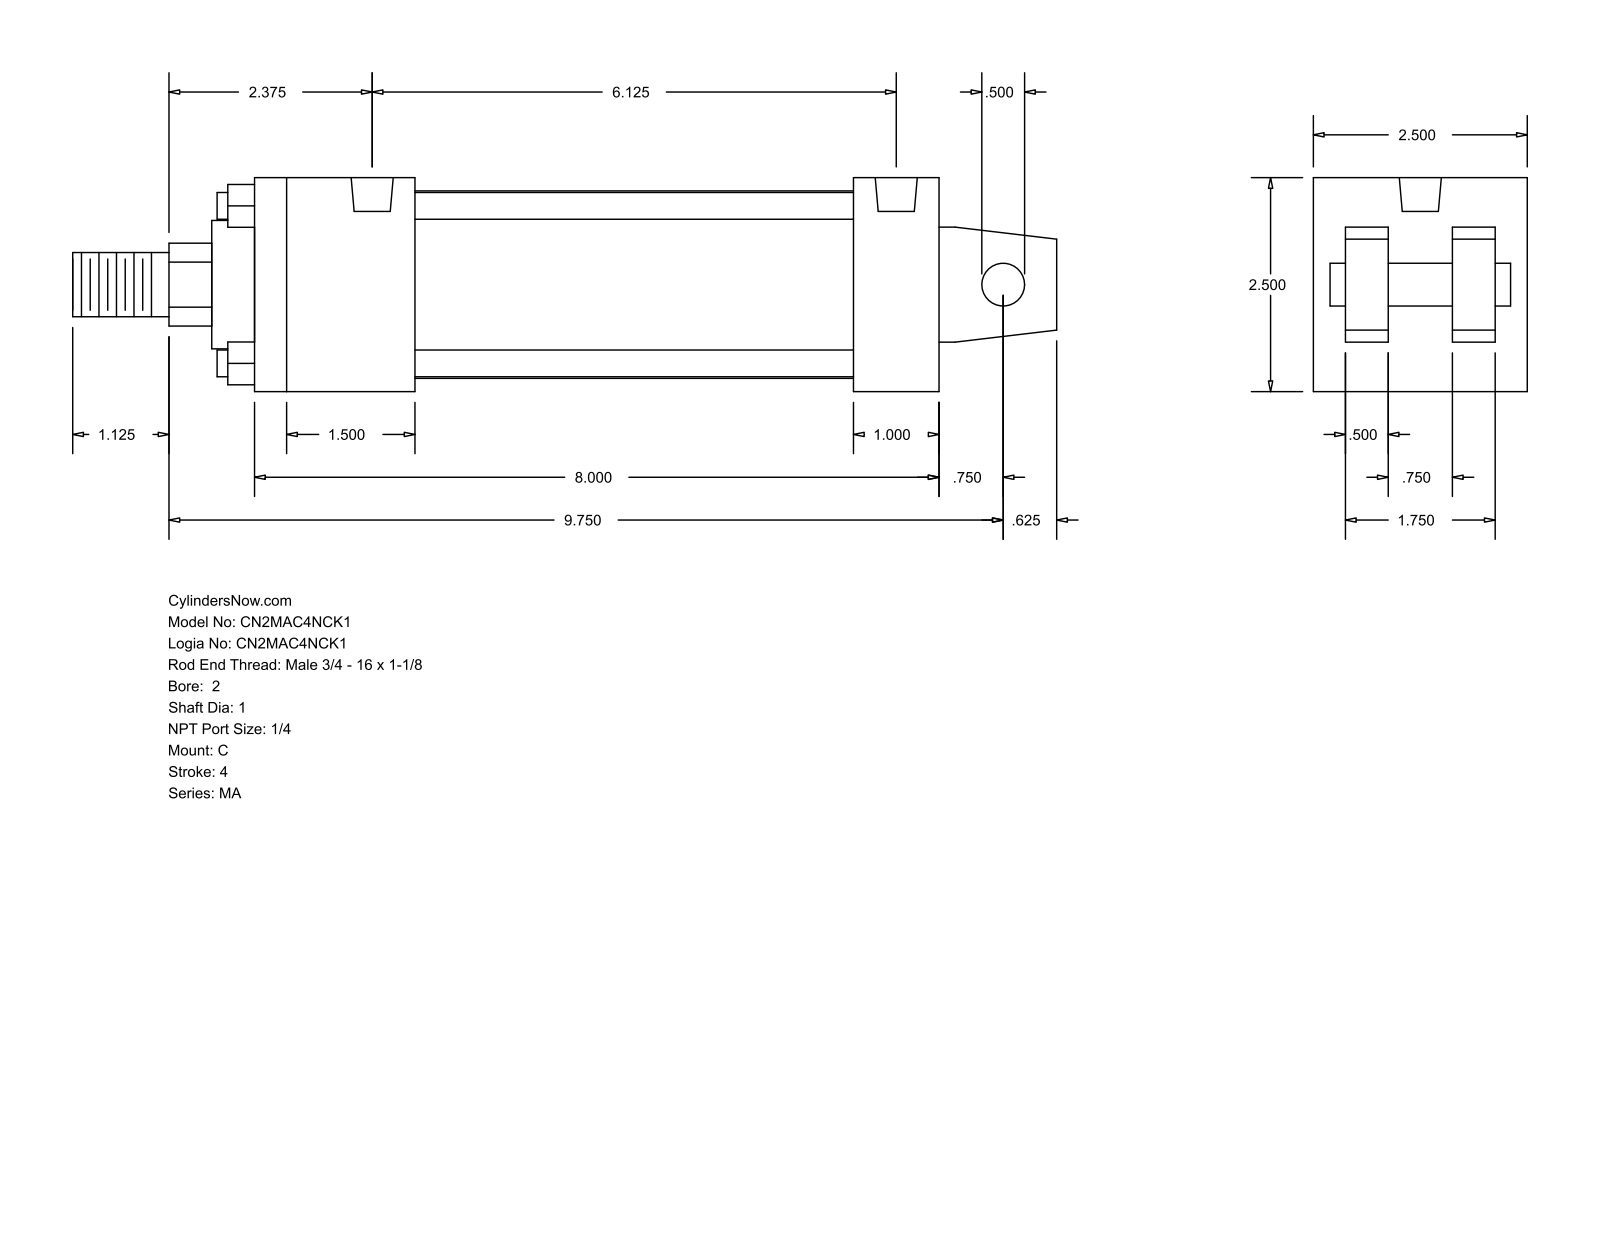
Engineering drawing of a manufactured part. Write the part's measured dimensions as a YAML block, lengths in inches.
part_name: "MA_C__0200_1"
step_written_by: "GSSL Pune (CONFIG_CONTROL_DESIGN)"
units: inches
bodies: {solids: 0, faces: 103, planar: 76, cylindrical: 27, other: 0}
overall_size: [11.5, 2.5, 2.5]
round_holes:
  - {diameter: 0.313, count: 4}
  - {diameter: 0.492, count: 2}
round_bosses_or_shafts:
  - {diameter: 0.313, count: 4}
  - {diameter: 2.19, count: 1}
  - {diameter: 1.5, count: 1}
  - {diameter: 1, count: 1}
  - {diameter: 0.75, count: 1}
  - {diameter: 0.5, count: 1}
partial_cylinders:
  - {radius: 0.484, count: 1}
face_to_face_distances: [2.5, 0.5, 8, 0.875, 1.625, 0.375, 2.125, 1.25, 1.875, 1]
hole_center_spacings: [6.125]
